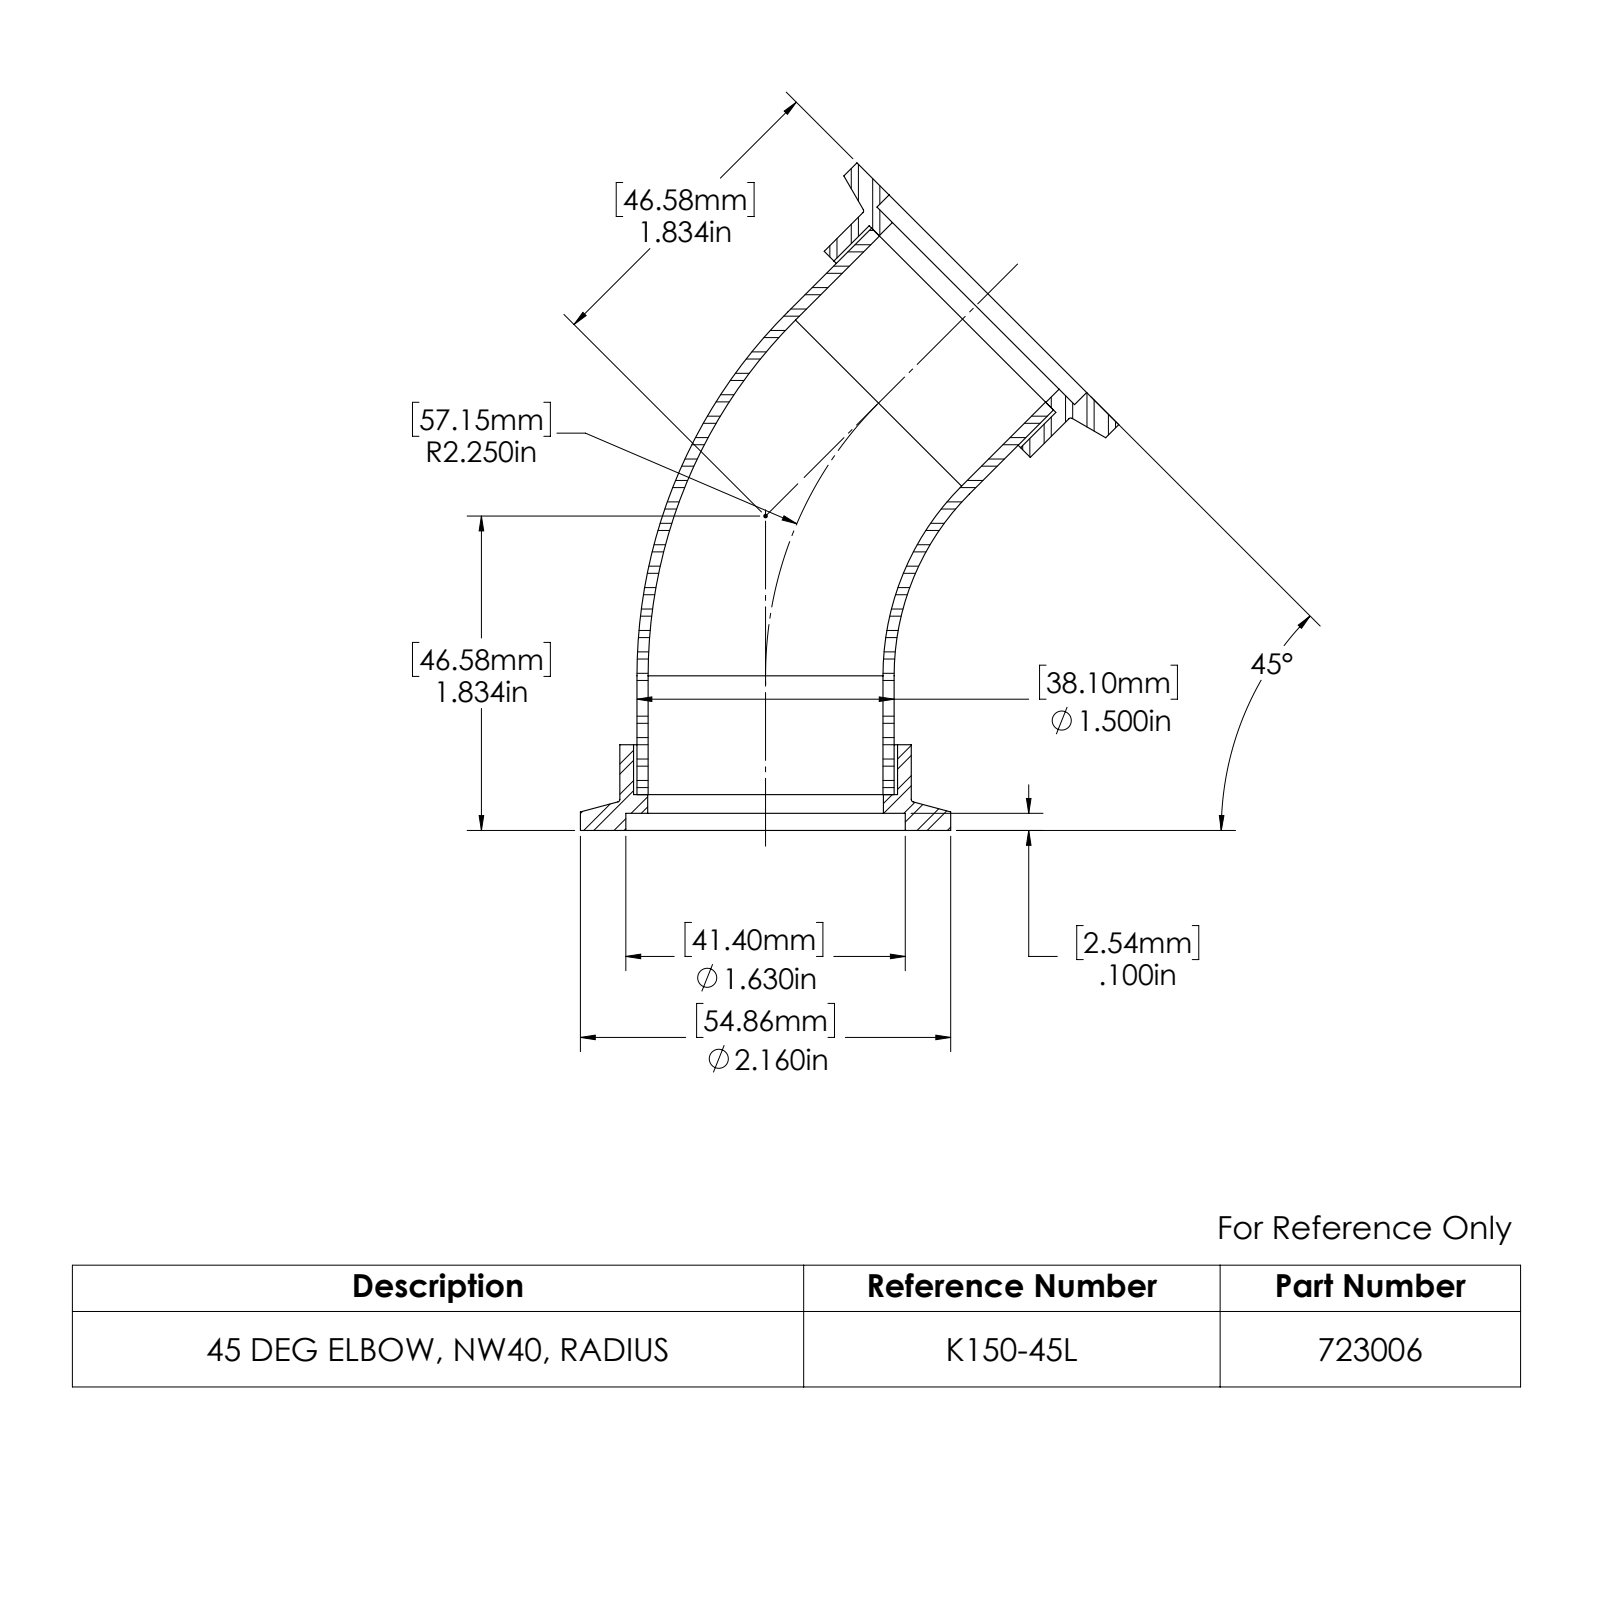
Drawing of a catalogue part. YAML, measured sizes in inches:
part_name: "972302; 403521; 723006-REV"
step_written_by: "SolidWorks 2022 (AUTOMOTIVE_DESIGN)"
units: inches
bodies: {solids: 3, faces: 50, planar: 10, cylindrical: 28, other: 12}
overall_size: [3.894, 3.141, 2.16]
volume: 1.753
surface_area: 47.57
round_holes:
  - {diameter: 1.37, count: 2}
  - {diameter: 1.375, count: 2}
  - {diameter: 1.54, count: 2}
  - {diameter: 1.63, count: 2}
round_bosses_or_shafts:
  - {diameter: 2.16, count: 2}
  - {diameter: 1.7, count: 2}
  - {diameter: 1.5, count: 2}
face_to_face_distances: [0.209, 0.1, 0.109, 0.5, 0.4, 0.291]
